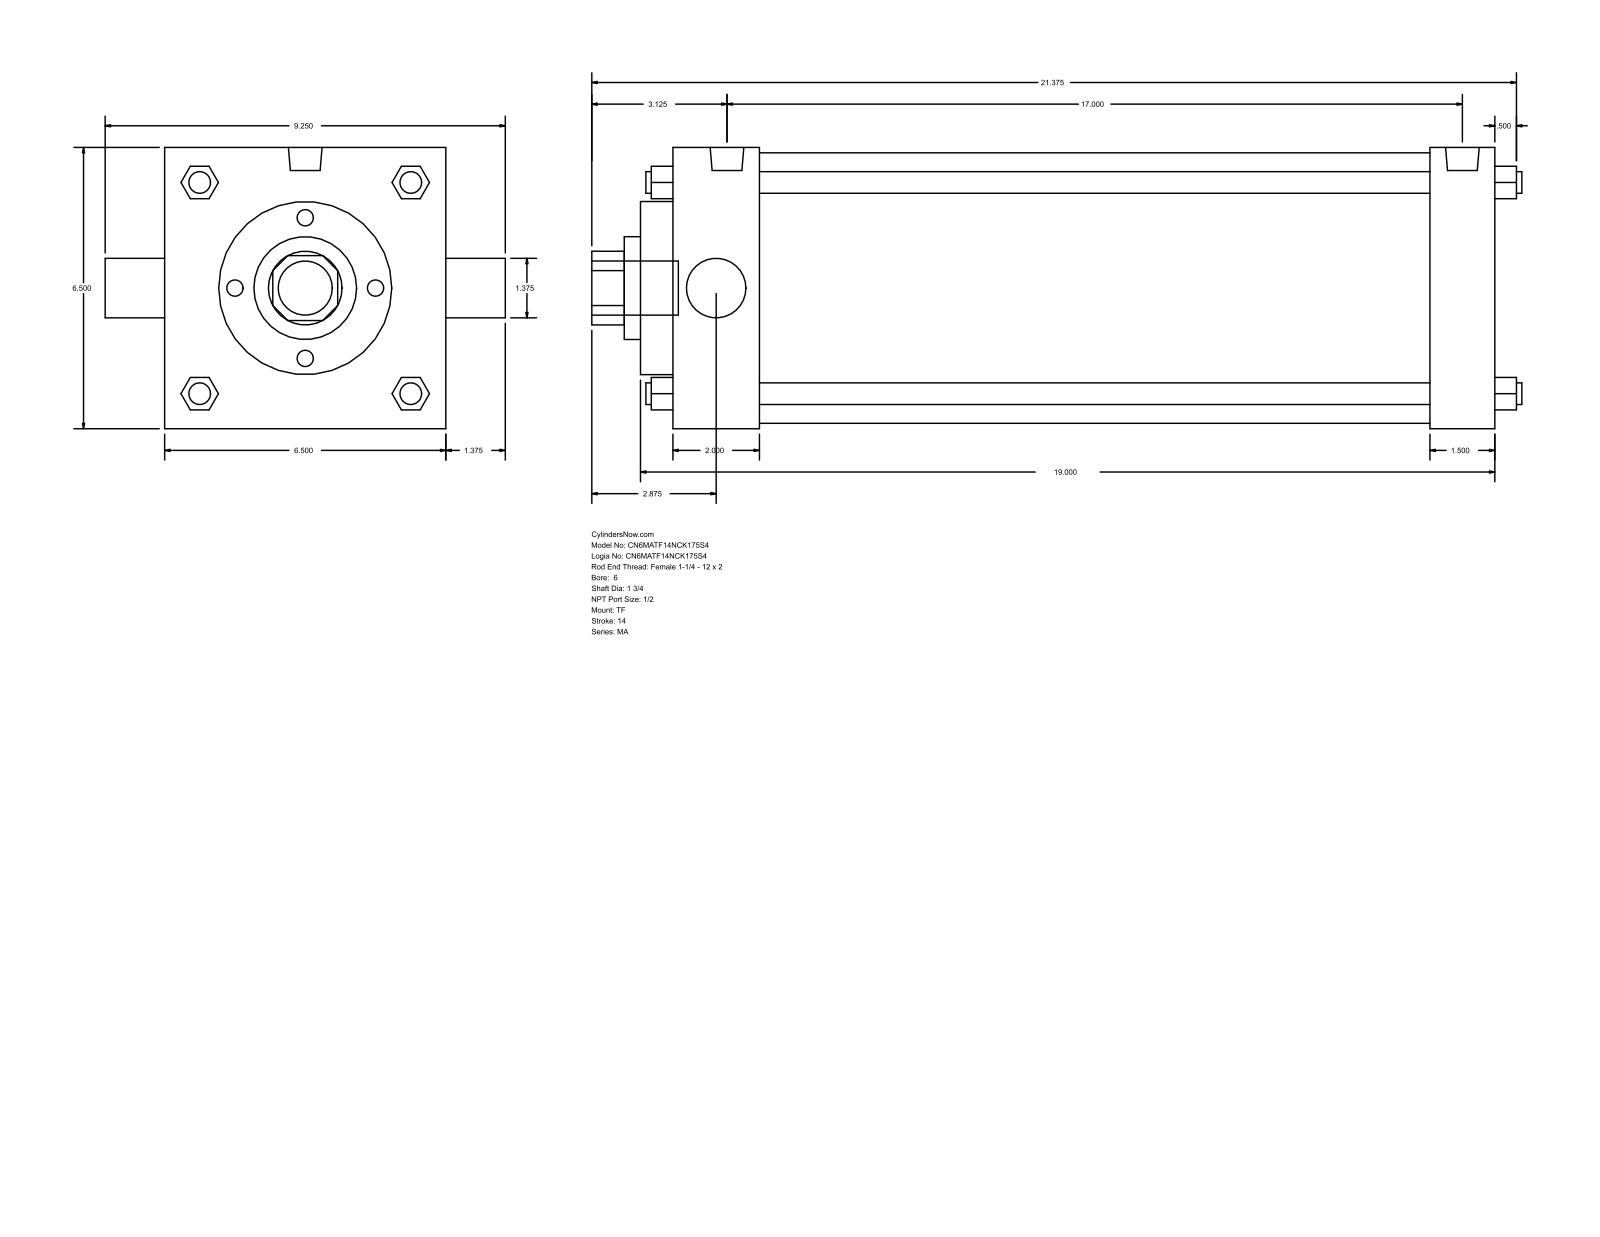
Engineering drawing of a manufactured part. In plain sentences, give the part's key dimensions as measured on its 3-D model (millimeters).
The part is named "MA_TF__0600_1.75". Its 3-D file was written by "GSSL Pune (CONFIG_CONTROL_DESIGN)". It is 0 solids with 122 faces: 93 planar, 29 cylindrical and 0 other. Overall it measures 546.1 by 234.95 by 165.1 millimeters. Round holes: 1 of diameter 34.92, 1 of diameter 44.45, 1 of diameter 60.33, 1 of diameter 101.6, 1 of diameter 158.75. Round bosses or shafts: 4 of diameter 12.7, 3 of diameter 17.46, 2 of diameter 19.77, 1 of diameter 31.75. Partial cylindrical surfaces (rounded edges, fillets, slot ends): 1 of radius 21.63. The main face-to-face distances are 165.1, 482.61, 19.05, 50.8, 444.5, 431.81, 393.7, 38.11, 69.85, 463.55.
